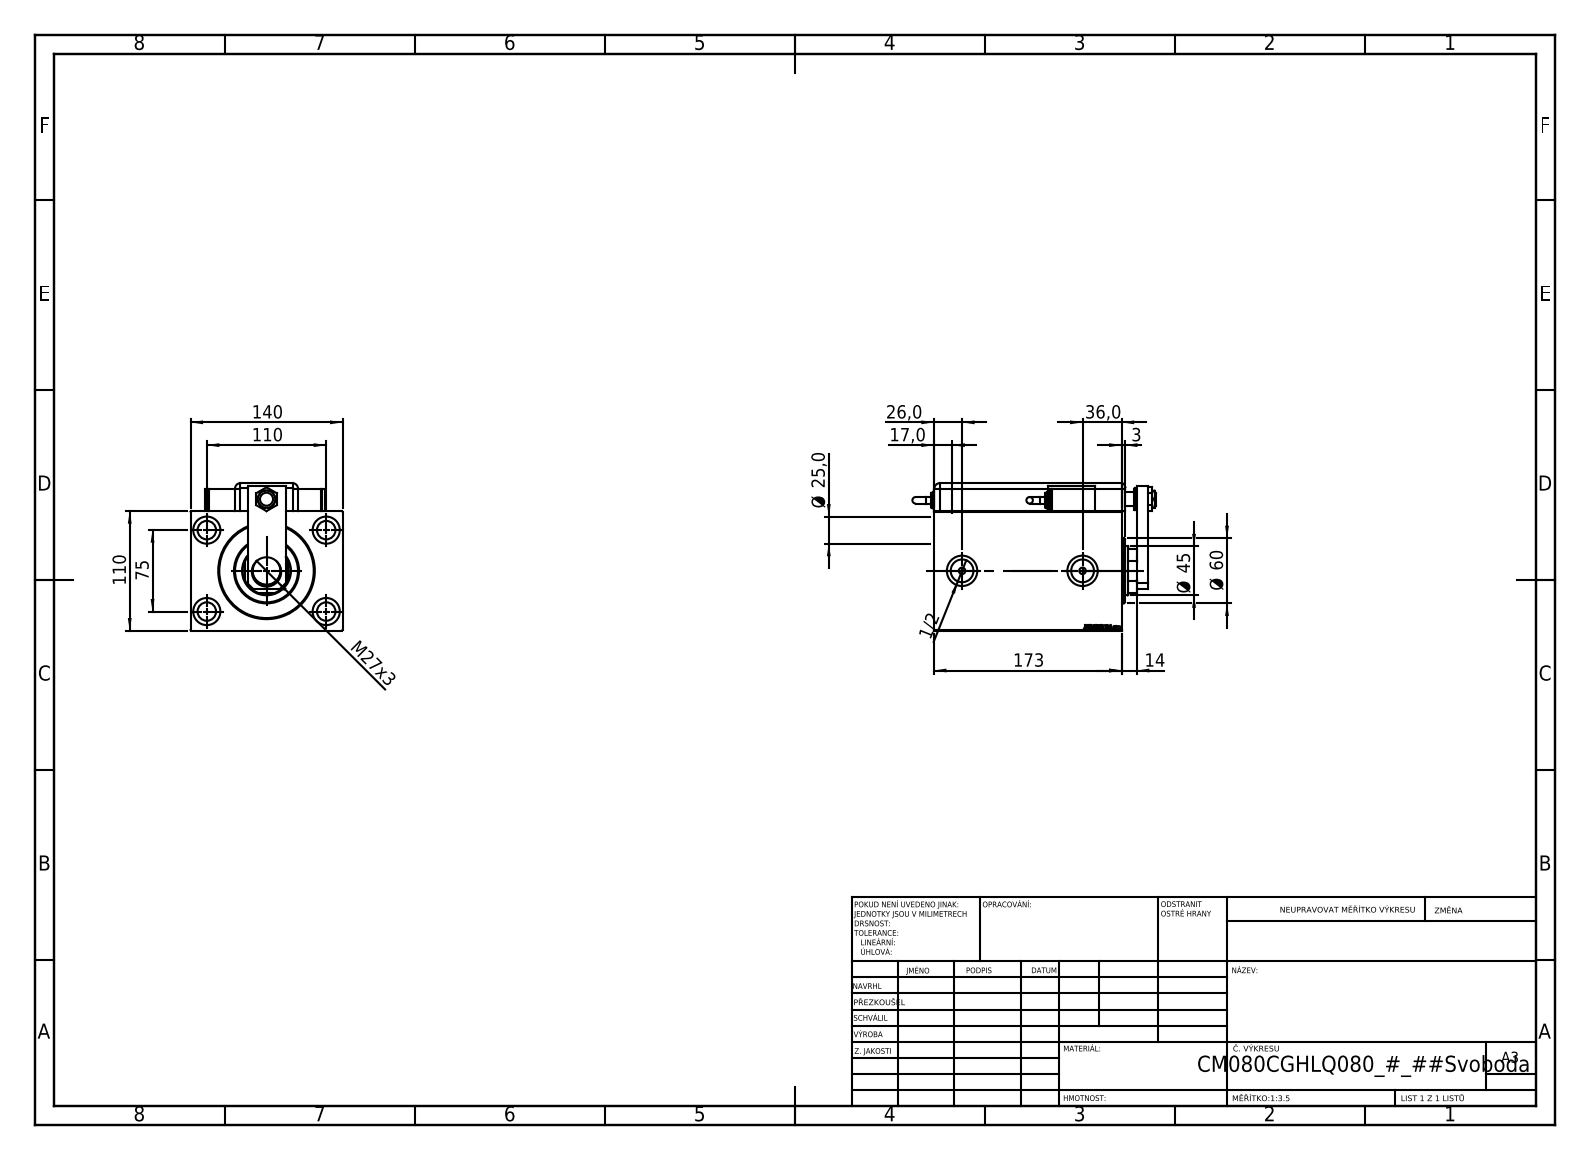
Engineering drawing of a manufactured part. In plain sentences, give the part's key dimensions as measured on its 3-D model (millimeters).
The part is named "NUT_D13; ZARAZKA_Q; SWITCH DIM A_G; KRYT (+7 more)". Its 3-D file was written by "SolidWorks 2019 (CONFIG_CONTROL_DESIGN)". It is 13 solids with 1246 faces: 614 planar, 115 cylindrical and 517 other. Overall it measures 224.46 by 140 by 135.8 millimeters. Its volume is 2 380 000 cubic millimeters and its surface area 329 453 square millimeters. Round holes: 4 of diameter 17, 4 of diameter 25, 2 of diameter 4, 2 of diameter 6, 2 of diameter 8, 2 of diameter 20.96, 2 of diameter 28, 1 of diameter 12, 1 of diameter 13, 1 of diameter 14, 1 of diameter 25.5, 1 of diameter 27. Round bosses or shafts: 3 of diameter 20, 2 of diameter 16, 2 of diameter 14, 2 of diameter 6, 1 of diameter 60. Partial cylindrical surfaces (rounded edges, fillets, slot ends): 9 of radius 5, 1 of radius 10, 1 of radius 22. The main face-to-face distances are 110, 140, 3, 173, 21, 152, 25.8, 135.8, 14, 41. The hole center spacings are 66.57, 61.95, 66.01, 67.14, 75, 110, 117.21, 133.14.
